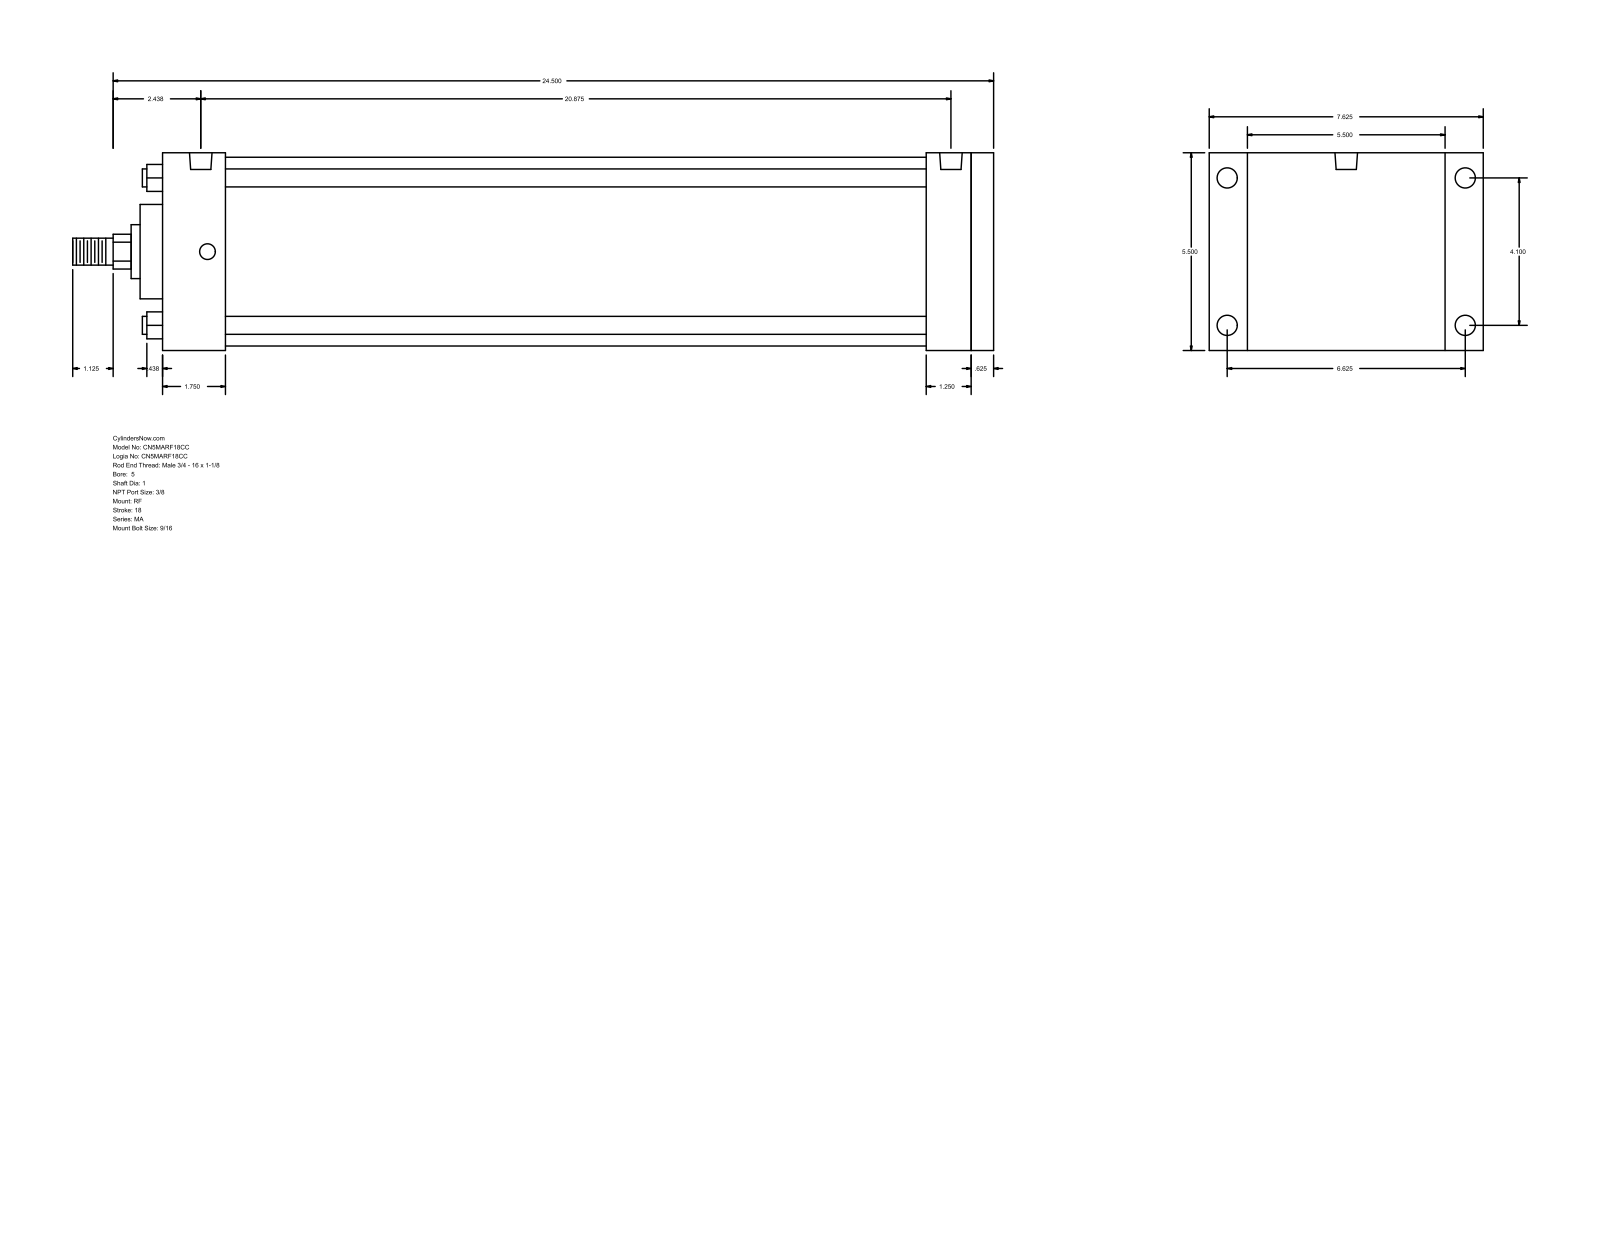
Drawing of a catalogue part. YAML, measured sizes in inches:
part_name: "MA_RF__0500_1"
step_written_by: "GSSL Pune (CONFIG_CONTROL_DESIGN)"
units: inches
bodies: {solids: 0, faces: 94, planar: 65, cylindrical: 29, other: 0}
overall_size: [25.625, 7.625, 5.5]
round_holes:
  - {diameter: 0.437, count: 4}
  - {diameter: 0.563, count: 4}
  - {diameter: 0.627, count: 2}
round_bosses_or_shafts:
  - {diameter: 0.5, count: 4}
  - {diameter: 5.25, count: 1}
  - {diameter: 2.625, count: 1}
  - {diameter: 1.5, count: 1}
  - {diameter: 1, count: 1}
  - {diameter: 0.75, count: 1}
partial_cylinders:
  - {radius: 0.484, count: 1}
face_to_face_distances: [5.5, 23.125, 22.5, 0.625, 1.75, 20.75, 21.375, 21.25, 19.5, 1.25]
hole_center_spacings: [0.187, 4.1, 6.625, 7.791, 20.5, 20.688, 20.875]
